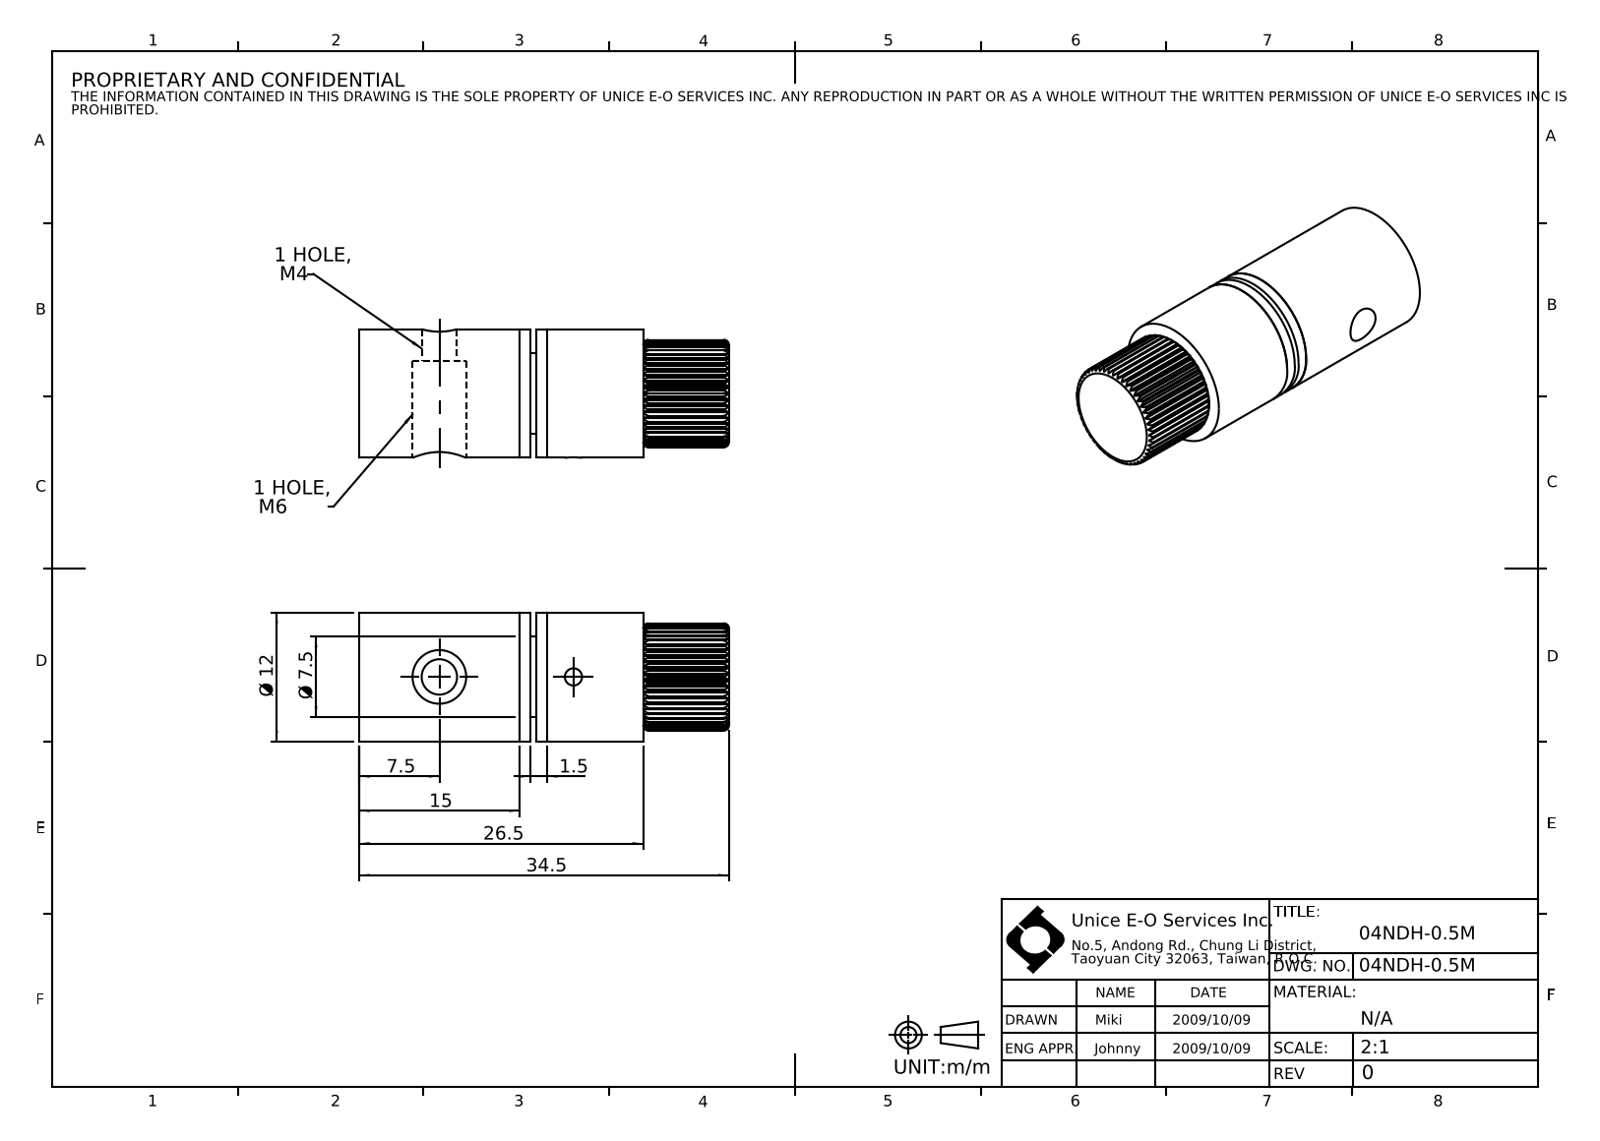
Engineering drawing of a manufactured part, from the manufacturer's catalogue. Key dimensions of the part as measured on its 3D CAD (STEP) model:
Part name (STEP PRODUCT): 04NDH-0.5M
STEP written by: SolidWorks 2016 (CONFIG_CONTROL_DESIGN)
Units: millimetres
Bodies: 5 solids, 267 faces (117 planar, 142 cylindrical, 8 other)
Overall size (bounding box): 34.5 × 12 × 12
Volume: 3 348 mm³ · Surface area: 2 888 mm²
Round holes (diameter × count): ⌀3.3 ×2, ⌀1.6 ×1, ⌀4.6 ×1, ⌀5 ×1, ⌀7.5 ×1, ⌀7.7 ×1
Round bosses / shafts (diameter × count): ⌀12 ×1, ⌀4 ×1
Partial cylindrical surfaces — rounded edges, fillets, slot ends (radius × count): R1 ×1, R5 ×1
Main face-to-face distances: 1, 1.5, 9, 2.5, 11.5, 6.72, 15, 17.5, 26.5, 16.5
Hole centre spacings: 12.5
